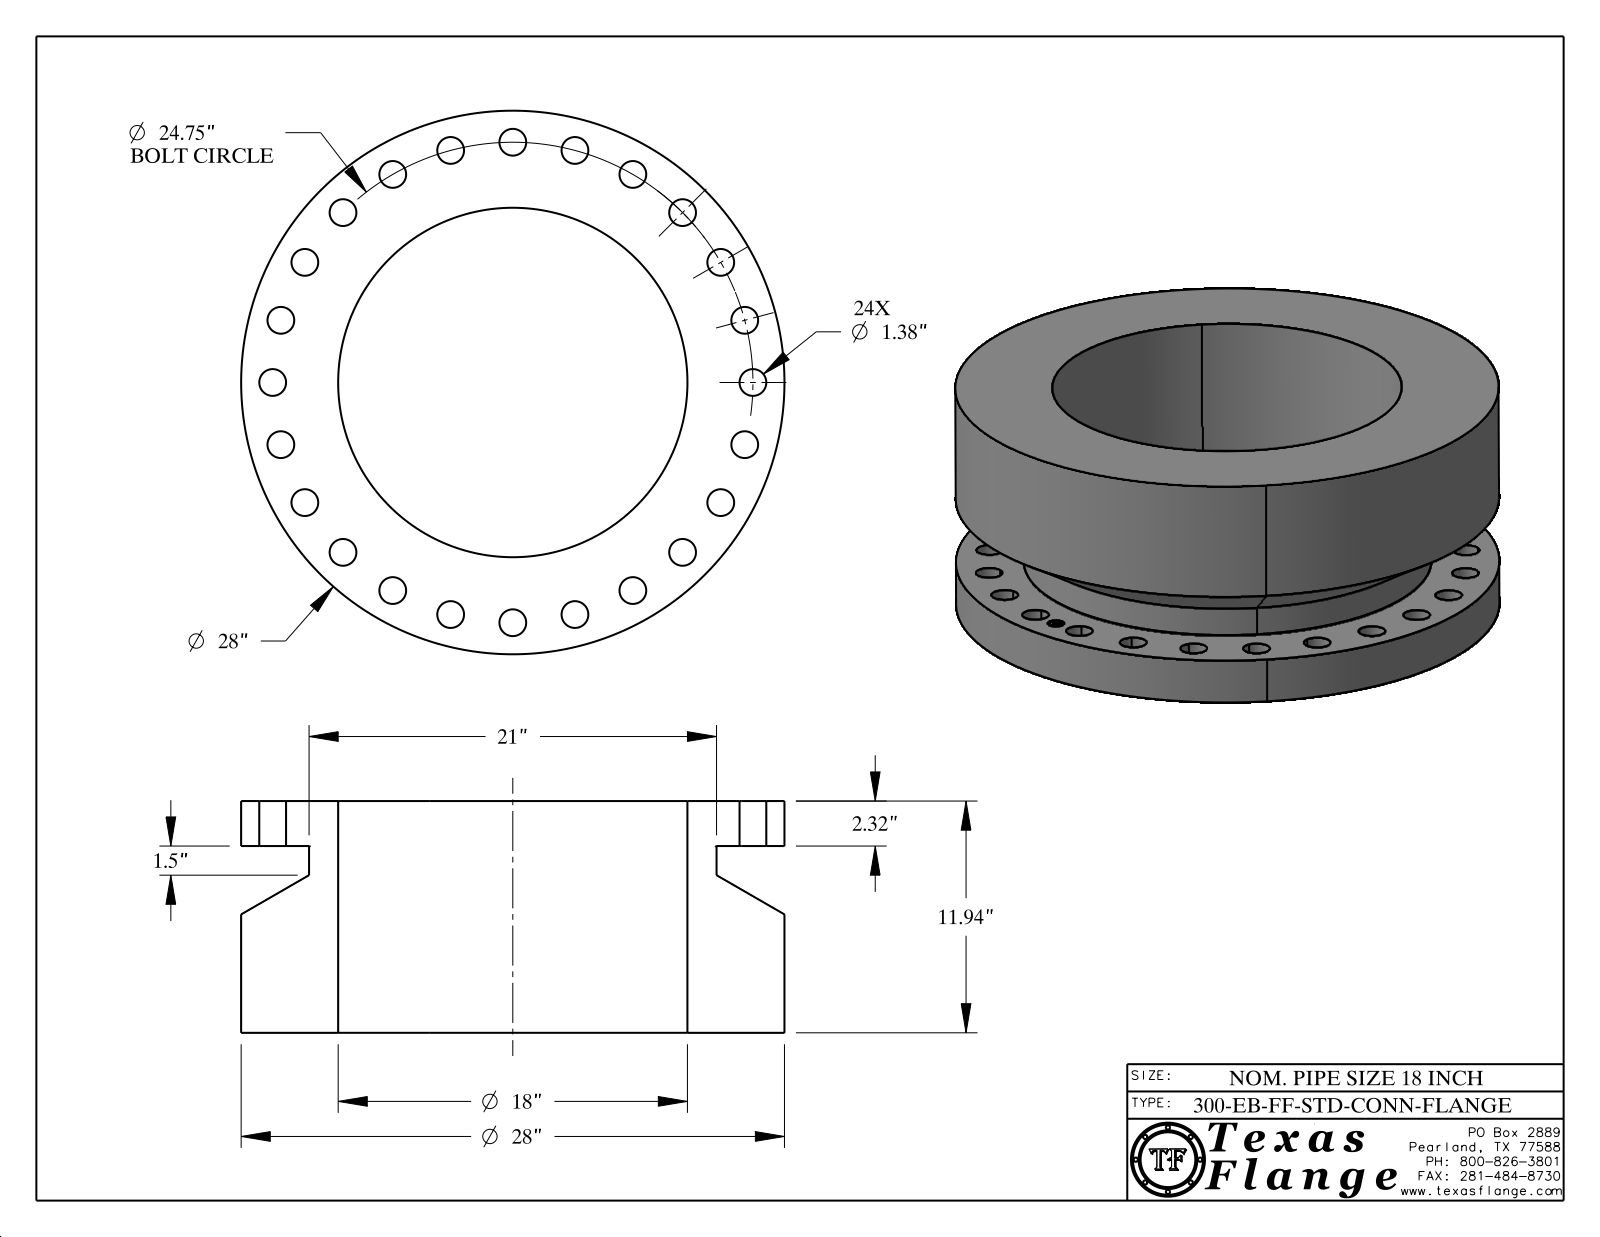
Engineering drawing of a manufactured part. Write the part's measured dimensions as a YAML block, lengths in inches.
part_name: "18-300-EB-FF-STD-CONN-FLANGE"
step_written_by: "CATIA V5 STEP AP214 (AUTOMOTIVE_DESIGN)"
units: inches
bodies: {solids: 1, faces: 450, planar: 368, cylindrical: 76, other: 6}
overall_size: [28, 28, 11.937]
volume: 3540
surface_area: 2989
round_holes:
  - {diameter: 1.38, count: 24}
  - {diameter: 0.85, count: 1}
  - {diameter: 18, count: 1}
round_bosses_or_shafts:
  - {diameter: 0.051, count: 8}
  - {diameter: 28, count: 1}
  - {diameter: 21, count: 1}
  - {diameter: 0.67, count: 1}
face_to_face_distances: [11.937, 2.317, 9.62, 2.313, 9.625, 0.253, 0.248, 0.046, 0.164, 0.211]
hole_center_spacings: [12.375, 9.471, 15.067, 17.501, 21.434, 22.866, 23.906, 3.23]
